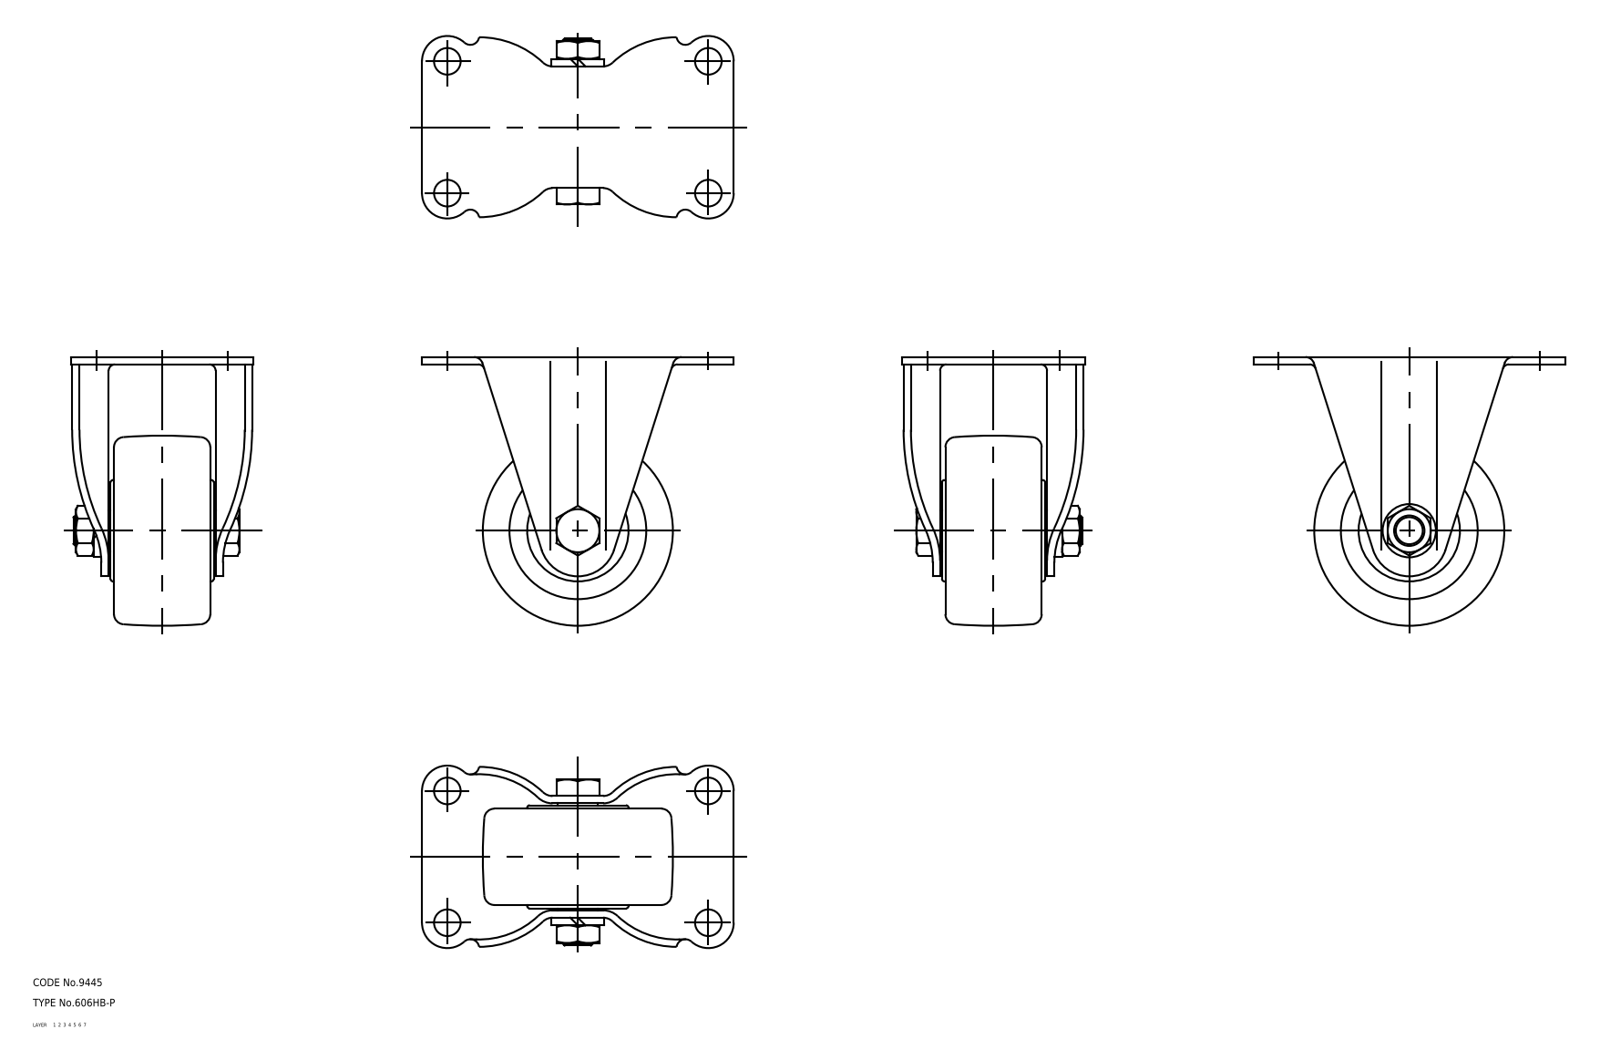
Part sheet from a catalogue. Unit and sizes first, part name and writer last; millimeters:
Units: millimetres
Overall size (bounding box): 123 × 106 × 72
Volume: 217 837 mm³ · Surface area: 56 000 mm²
Bodies: 3 solids, 164 faces (0 planar, 0 cylindrical, 164 other)
Part name (STEP PRODUCT): 67119388; 67119401; 67119414
STEP written by: CADfix (AUTOMOTIVE_DESIGN)
